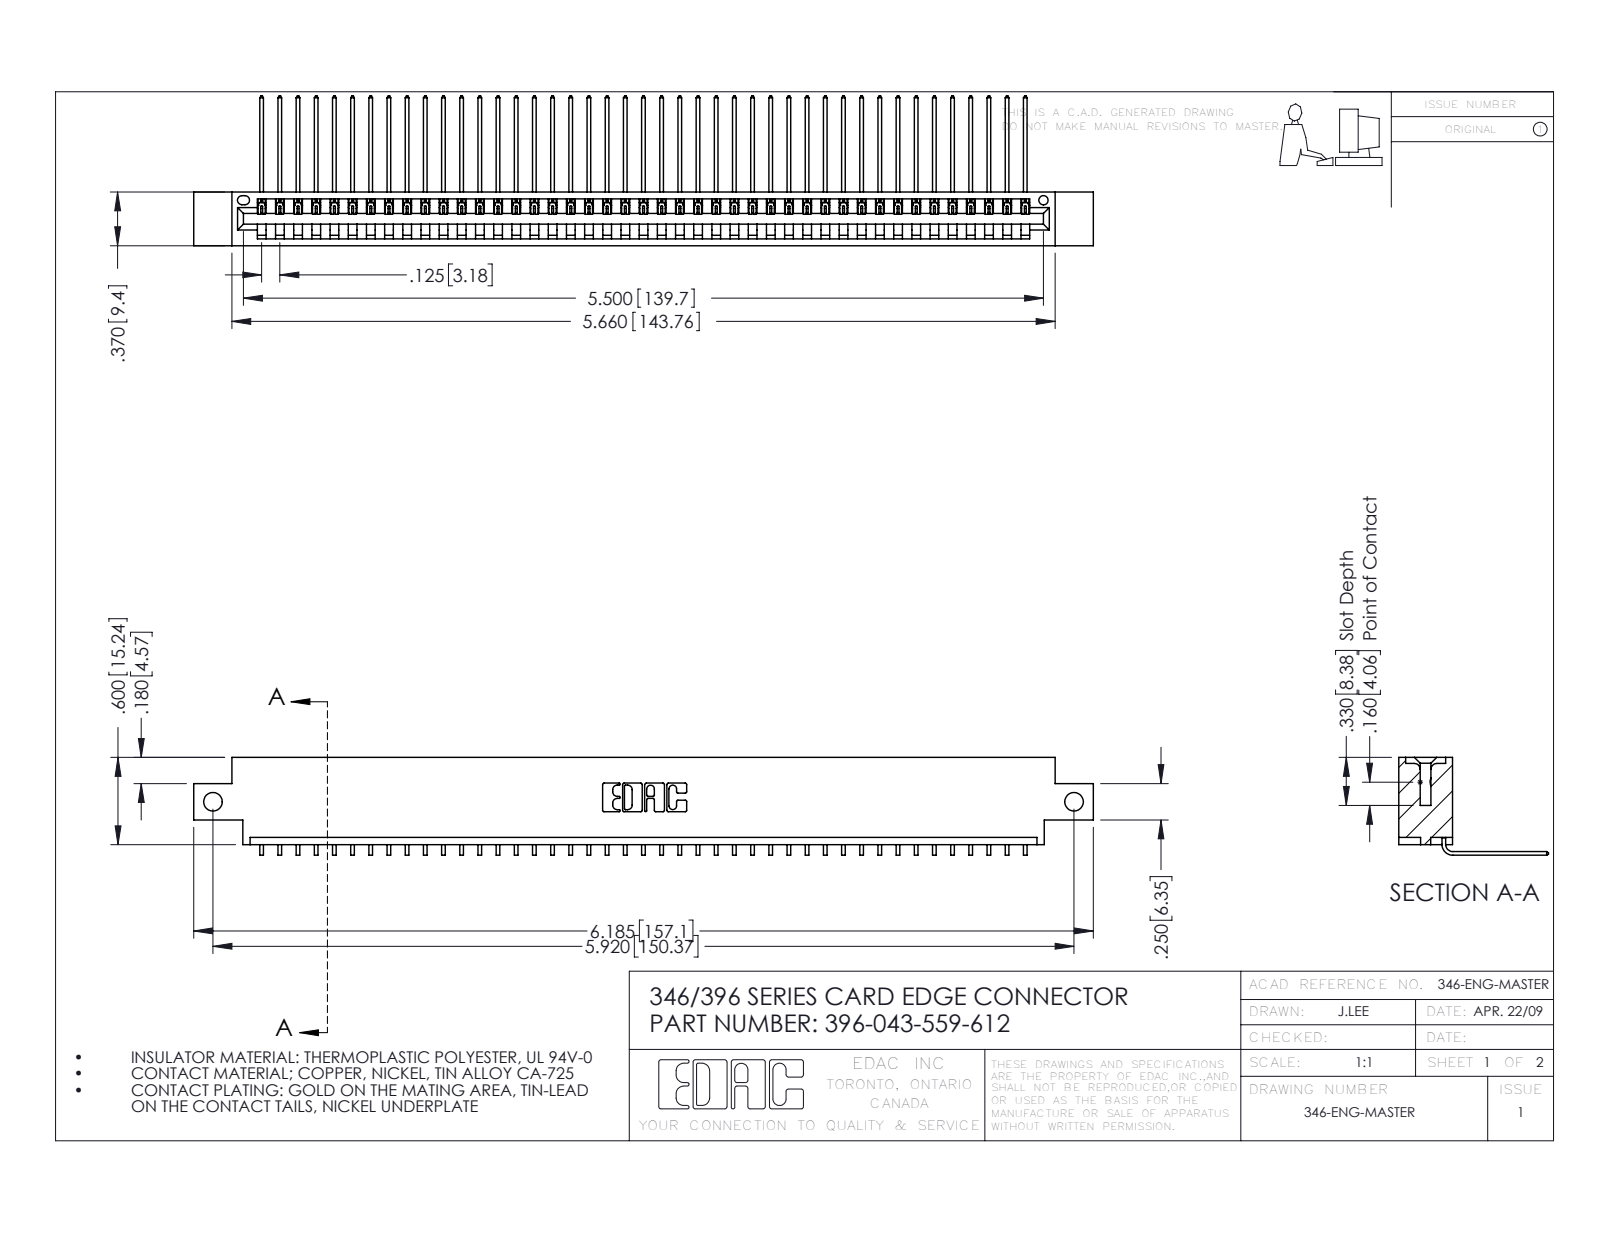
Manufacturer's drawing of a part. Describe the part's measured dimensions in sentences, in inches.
The part is named "396-043-559-612; 345-292-001_558 559 Tail - 1; 346 Part_0.170 Offset - Side Mount". Its 3-D file was written by "SolidWorks 2016 (CONFIG_CONTROL_DESIGN)". It is 44 solids with 2706 faces: 1886 planar, 820 cylindrical and 0 other. Overall it measures 6.185 by 1.03 by 0.673 inches. Its volume is 0.912 cubic inches and its surface area 30.32 square inches. Round holes: 2 of diameter 0.128, 1 of diameter 0.064. Partial cylindrical surfaces (rounded edges, fillets, slot ends): 86 of radius 0.006, 22 of radius 0.01, 6 of radius 0.007, 6 of radius 0.031, 3 of radius 0.026, 2 of radius 0.031, 2 of radius 0.04, 1 of radius 0.014. The main face-to-face distances are 0.048, 0.322, 0.37, 0.25, 0.025, 0.072, 0.298, 0.148, 0.222, 0.1. The hole center spacings are 5.92.
